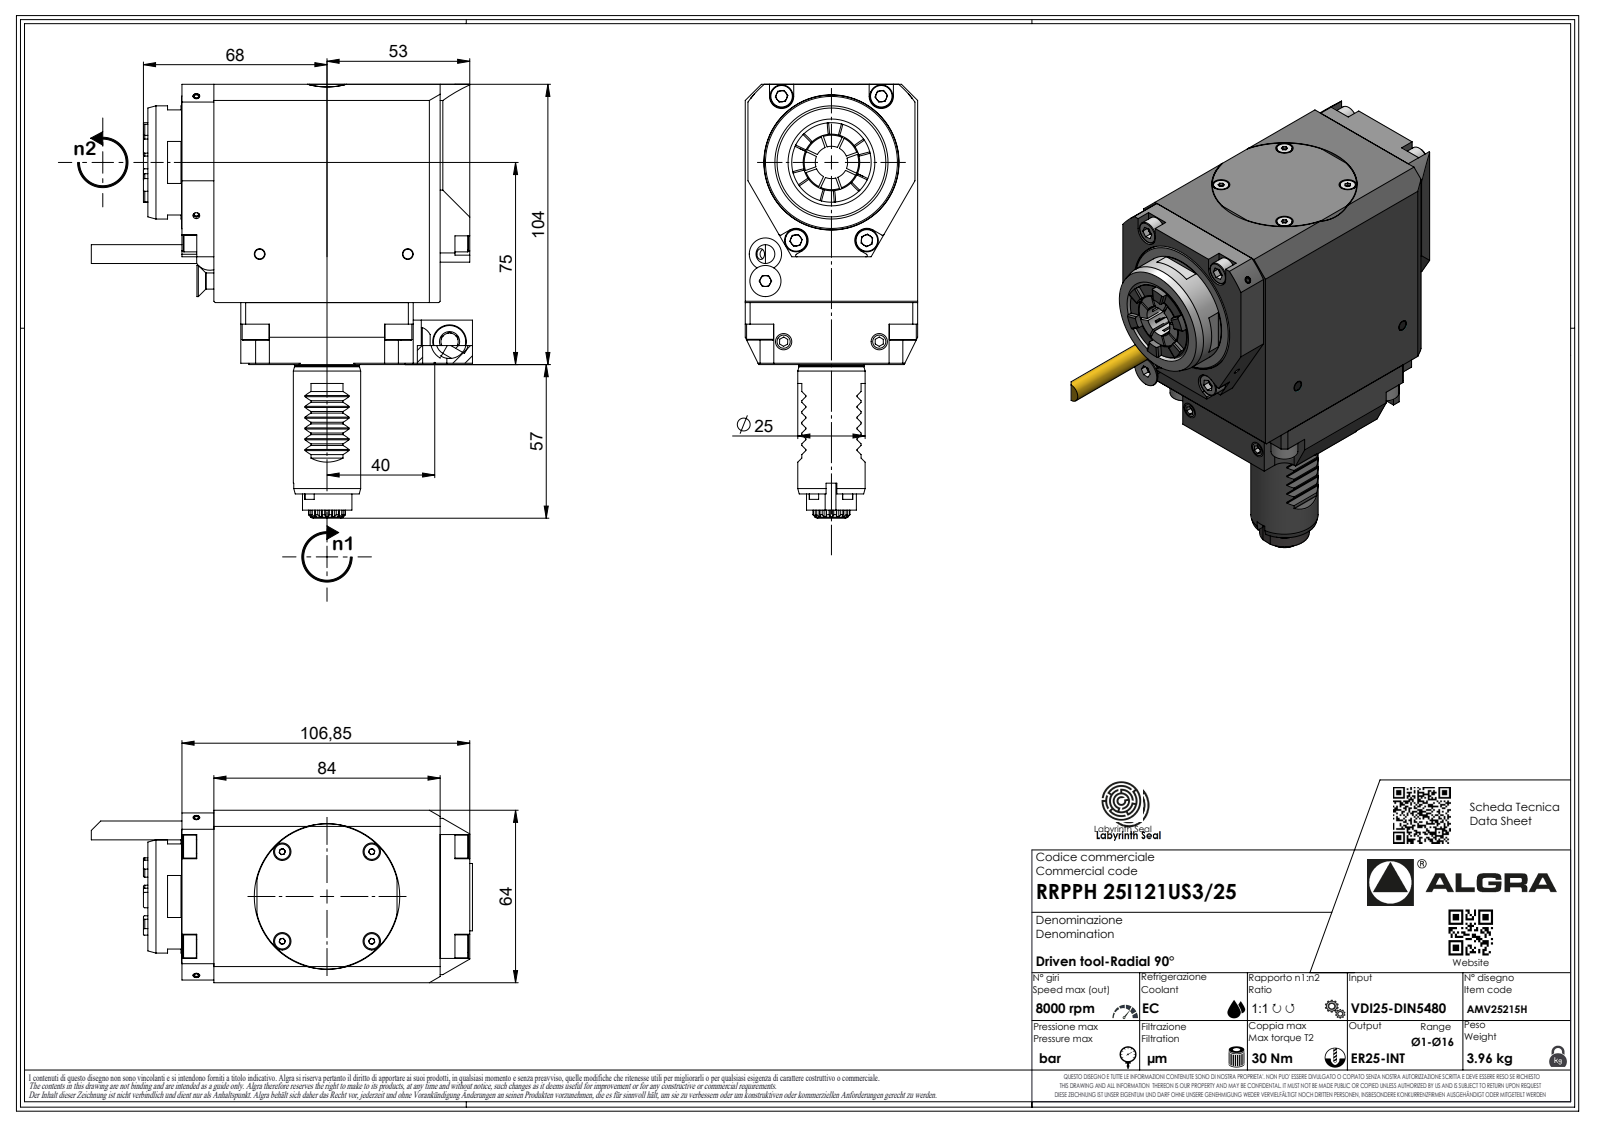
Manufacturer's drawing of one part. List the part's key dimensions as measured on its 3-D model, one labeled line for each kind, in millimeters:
Part name (STEP PRODUCT): RRPPH25I121US325
STEP written by: SolidWorks 2023 (AUTOMOTIVE_DESIGN)
Units: millimetres
Bodies: 1 solid, 816 faces (510 planar, 144 cylindrical, 162 other)
Overall size (bounding box): 161 × 145.5 × 64
Volume: 640 589 mm³ · Surface area: 57 537 mm²
Round holes (diameter × count): ⌀2.1 ×1, ⌀4 ×1, ⌀18.7 ×1, ⌀21 ×1, ⌀22 ×1, ⌀30.5 ×1
Round bosses / shafts (diameter × count): ⌀42 ×1, ⌀29.5 ×1, ⌀25 ×1, ⌀24.1 ×1, ⌀19.27 ×1, ⌀18.5 ×1, ⌀7 ×1, ⌀6.37 ×1
Partial cylindrical surfaces — rounded edges, fillets, slot ends (radius × count): R0.3 ×12, R35 ×8, R0.33 ×7, R0.52 ×7, R3.7 ×7, R0.5 ×6, R4.5 ×4, R5.1 ×4
Main face-to-face distances: 64, 104, 10, 74, 23, 95.85, 95, 84, 0.5, 6.5
